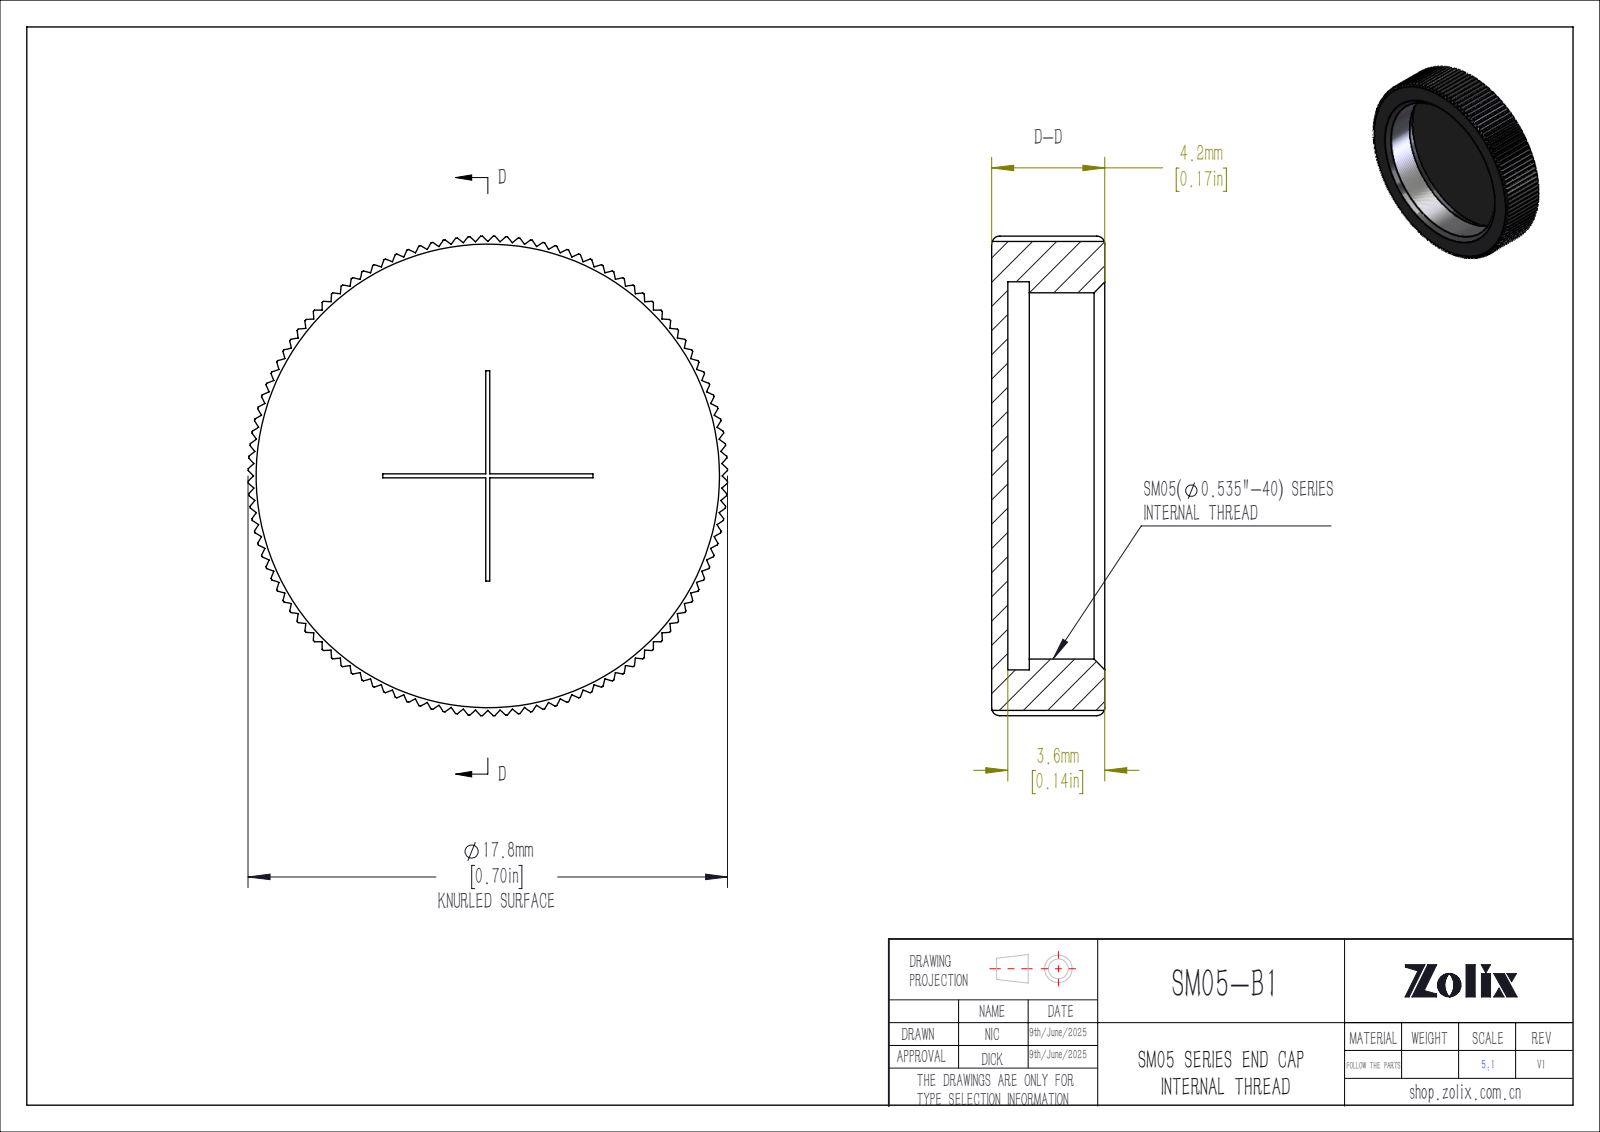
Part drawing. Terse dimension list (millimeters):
name: SM05-B1
written by: SolidWorks 2020 (CONFIG_CONTROL_DESIGN)
unit: mm
bodies: 1 solid, 658 faces (463 planar, 124 cylindrical, 71 other)
size: 17.8 × 17.8 × 4.2
volume: 484 mm³; area: 978 mm²
holes: 1× ⌀13.59, 1× ⌀14.4
rounds: 1× R8.9
face distances: 0.6, 12.3, 4.2, 3.6, 12.31, 1.4, 0.8, 2.8, 0.58, 1.38
